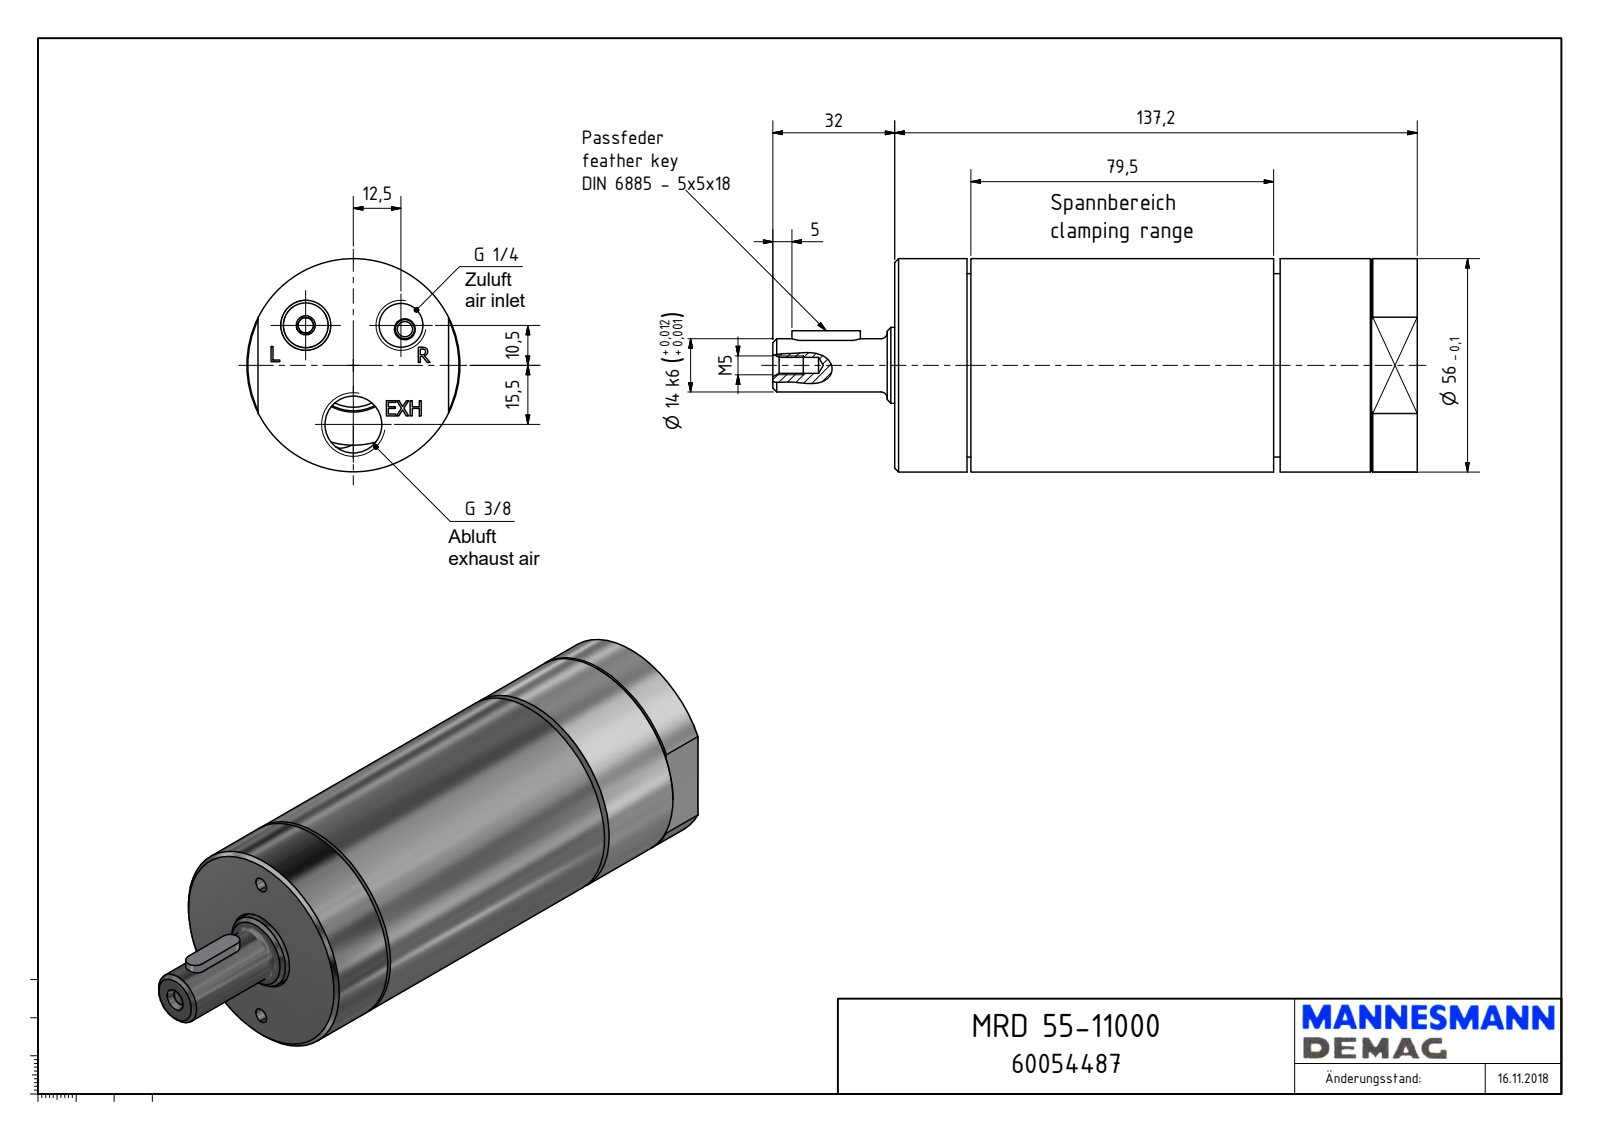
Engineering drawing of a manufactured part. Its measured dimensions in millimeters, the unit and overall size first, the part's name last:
Units: millimetres
Overall size (bounding box): 169.2 × 56 × 56
Round holes (diameter × count): ⌀4 ×3, ⌀4.13 ×1, ⌀11.45 ×1, ⌀14.95 ×1, ⌀21 ×1, ⌀21.25 ×1, ⌀23.54 ×1, ⌀26 ×1, ⌀48.38 ×1
Round bosses / shafts (diameter × count): ⌀56 ×1, ⌀48.18 ×1, ⌀19.95 ×1, ⌀14 ×1
Partial cylindrical surfaces — rounded edges, fillets, slot ends (radius × count): R2.5 ×2, R6 ×2, R5.72 ×1, R19.55 ×1, R23 ×1
Main face-to-face distances: 137.2, 20, 117.2, 99.5, 79.5, 37.7, 1, 19, 101.2, 80.5
Hole centre spacings: 16.32, 21, 28.85, 33.89, 5.5, 15.5, 25, 36.5
Volume: 335 295 mm³ · Surface area: 38 346 mm²
Bodies: 1 solid, 189 faces (103 planar, 34 cylindrical, 52 other)
Part name (STEP PRODUCT): MRD 55-11000_60054487
STEP written by: Autodesk Inventor 2018 (AUTOMOTIVE_DESIGN)
